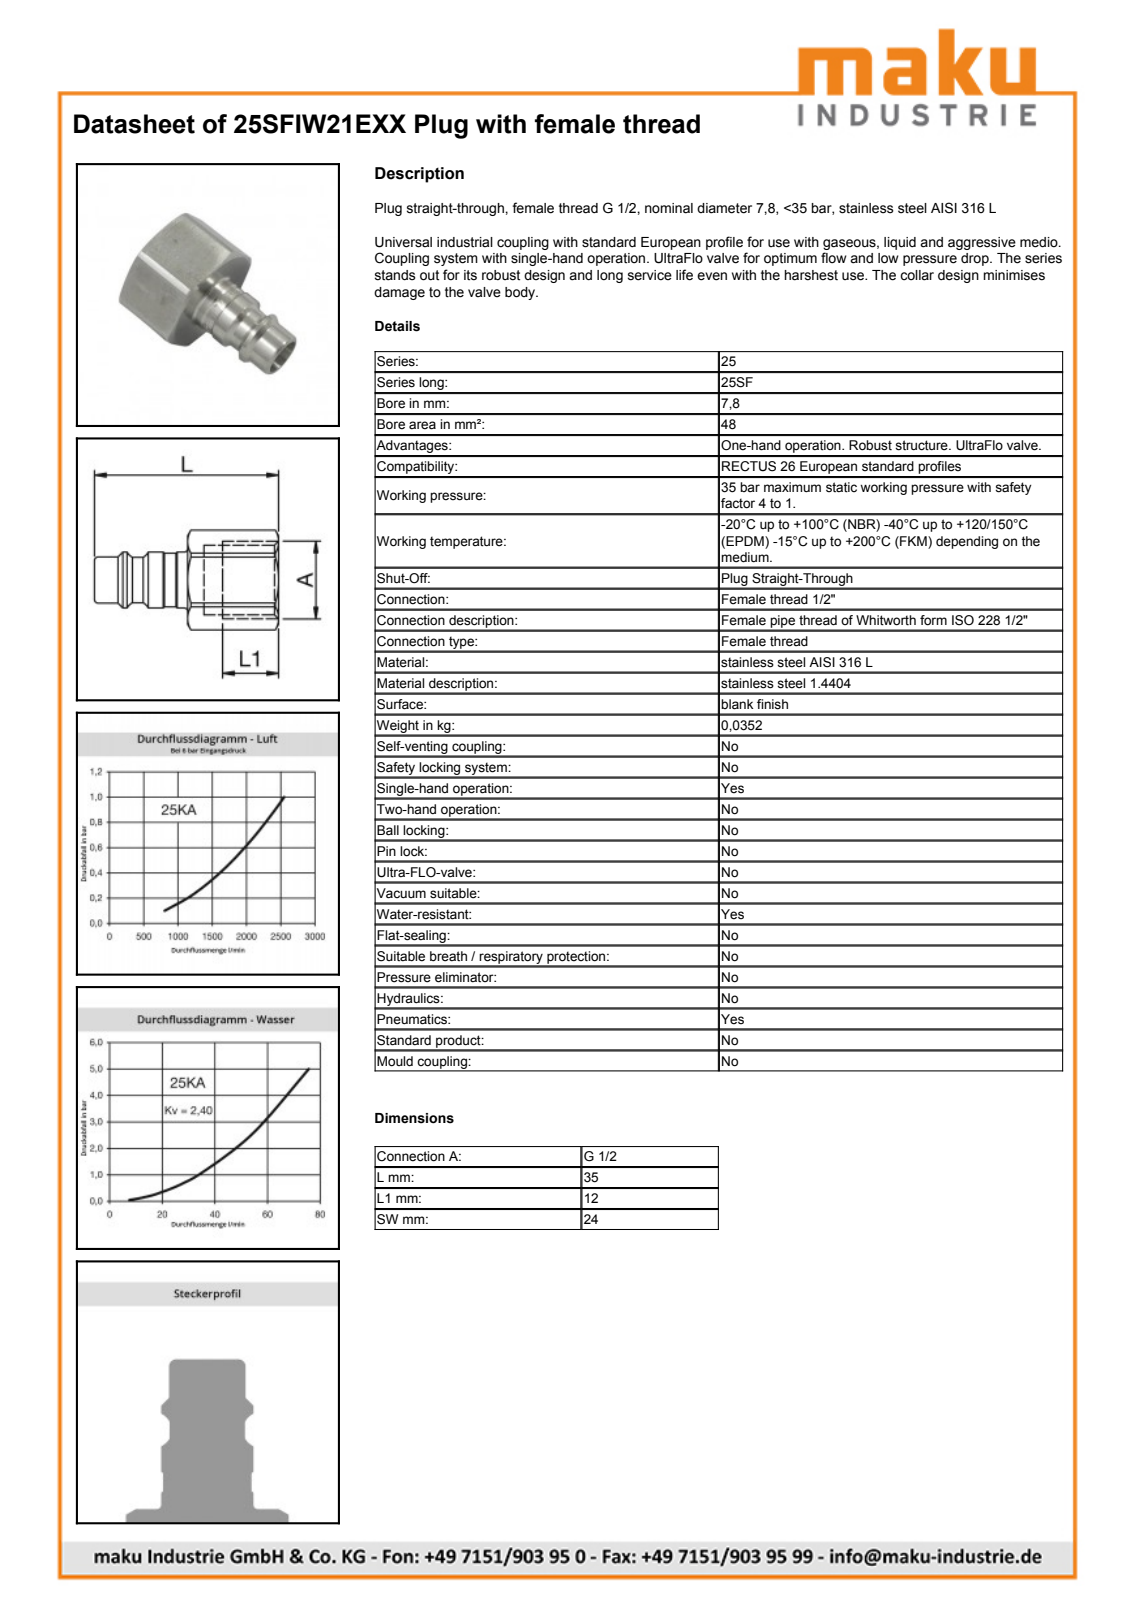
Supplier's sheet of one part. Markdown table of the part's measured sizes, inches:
| quantity | value |
| --- | --- |
| part name | D105657 |
| STEP written by | Autodesk Inventor 2011 (AUTOMOTIVE_DESIGN) |
| units | inches |
| bodies | 1 solid, 41 faces (10 planar, 12 cylindrical, 19 other) |
| overall size | 1.378 × 1.065 × 0.945 |
| volume | 0.302 in³ |
| surface area | 6.226 in² |
| round holes (diameter × count) | 0.309 × 1, 0.733 × 1 |
| round bosses / shafts (diameter × count) | 0.472 × 1, 0.39 × 1, 0.384 × 1 |
| partial cylindrical surfaces (radius × count) | 0.533 × 1 |
| main face-to-face distances | 0.945, 0.118, 0.591, 0.472, 0.787, 0.906, 1.378 |
